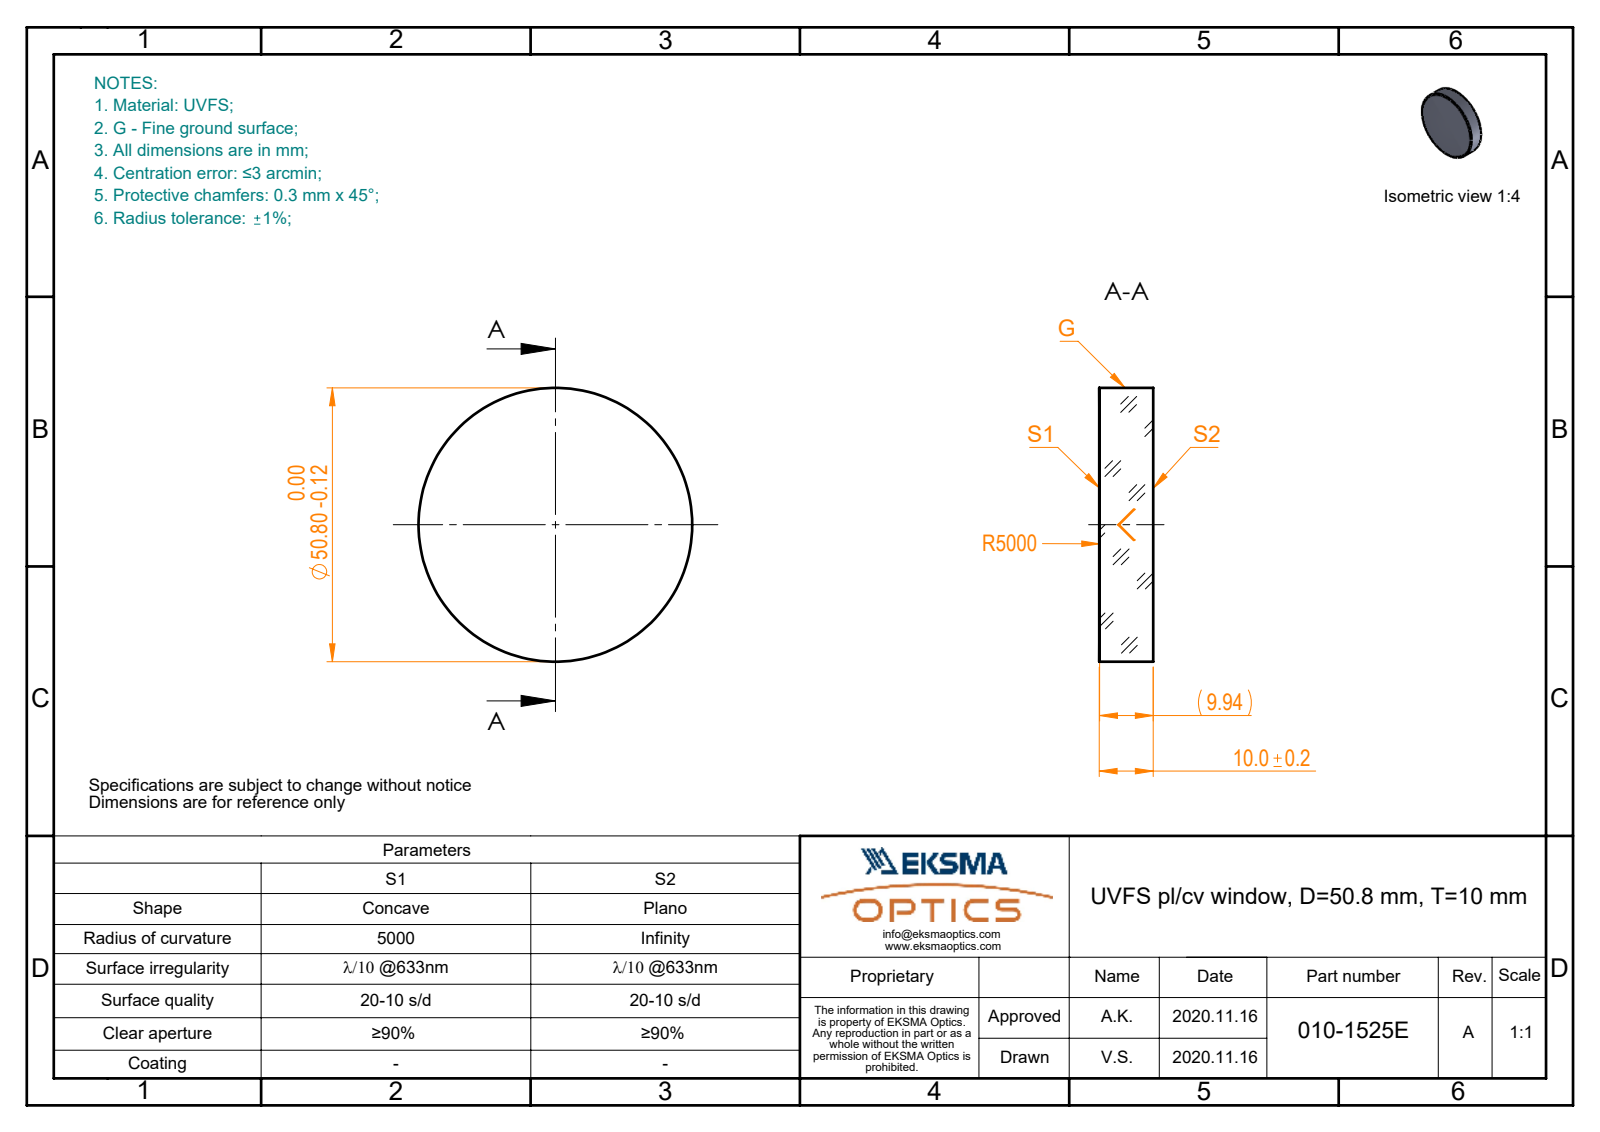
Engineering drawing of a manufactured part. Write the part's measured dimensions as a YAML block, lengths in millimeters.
part_name: "010-1525E_UVFS_PCV_window"
step_written_by: "SolidWorks 2019 (CONFIG_CONTROL_DESIGN)"
units: millimeters
bodies: {solids: 1, faces: 5, planar: 1, cylindrical: 2, other: 2}
overall_size: [50.8, 50.8, 10]
volume: 20203
surface_area: 5650
round_bosses_or_shafts:
  - {diameter: 50.8, count: 1}
